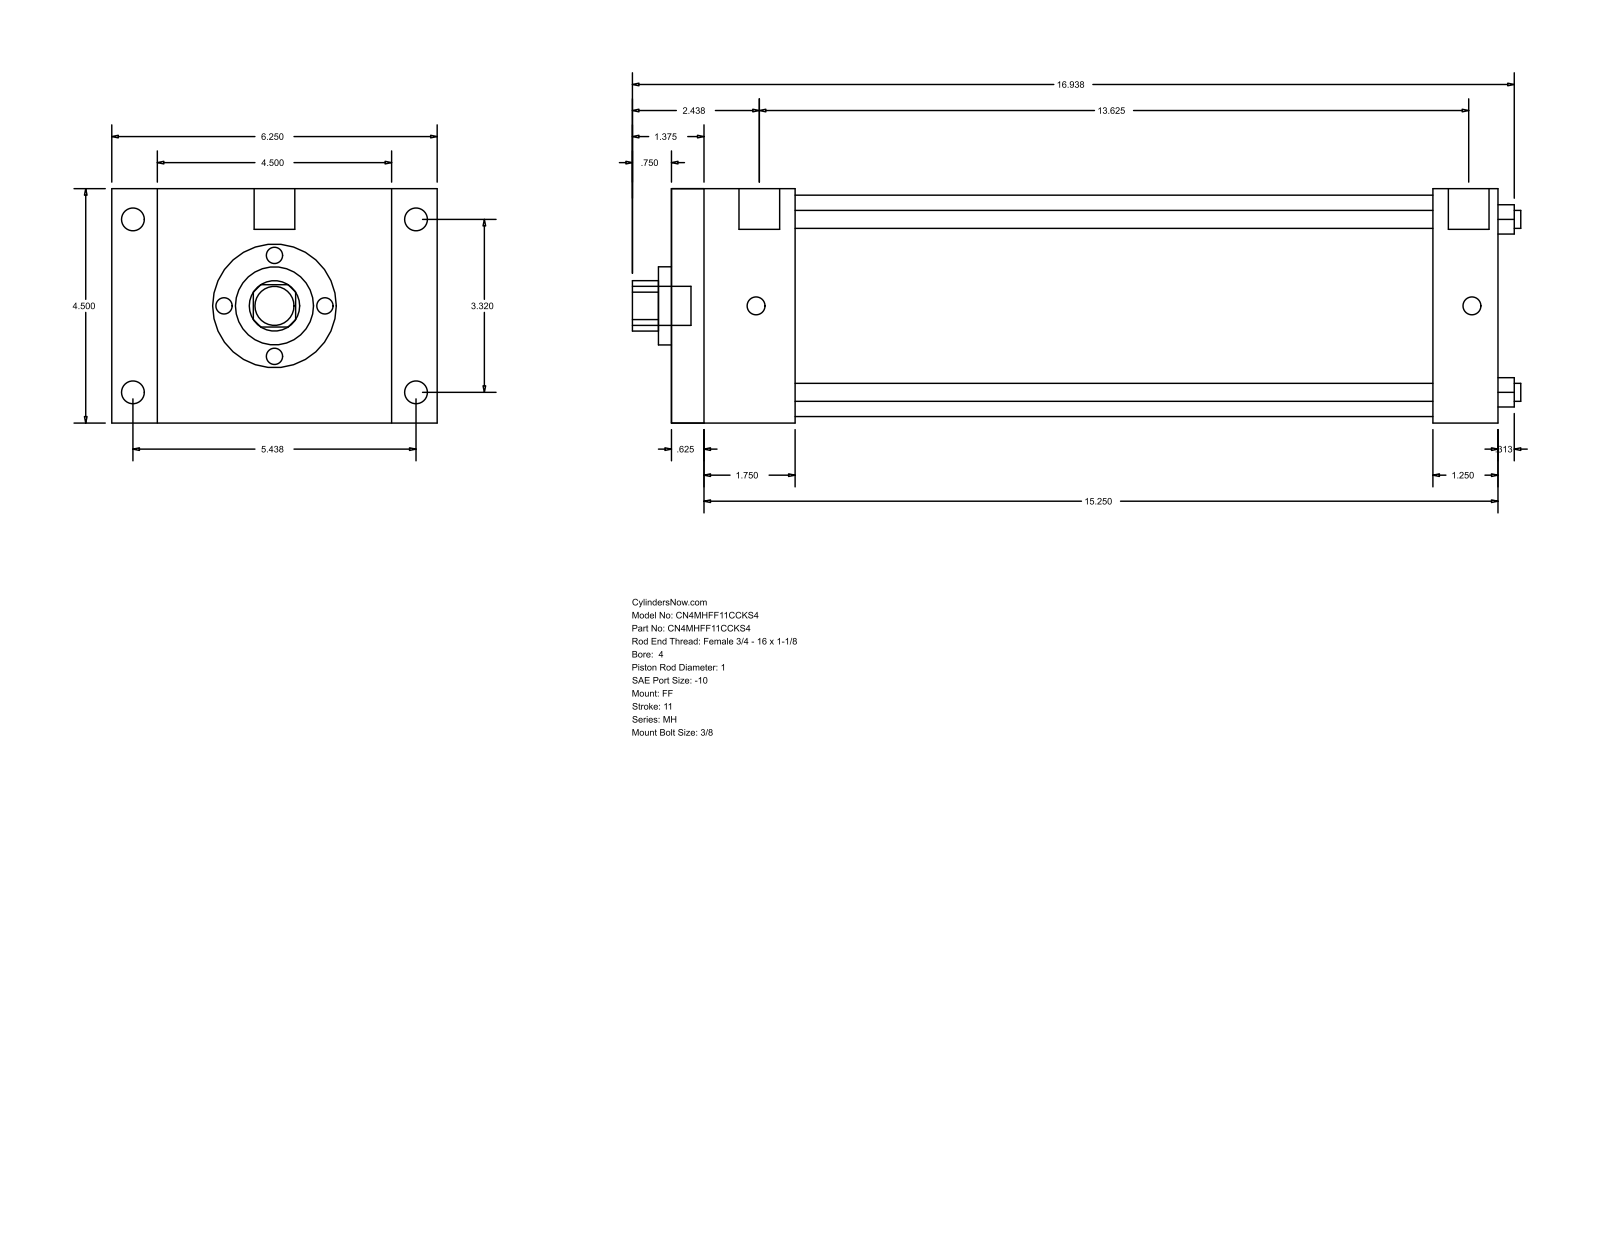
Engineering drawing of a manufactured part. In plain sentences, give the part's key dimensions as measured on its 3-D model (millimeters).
The part is named "MH_FF__0400_1". Its 3-D file was written by "GSSL Pune (CONFIG_CONTROL_DESIGN)". It is 0 solids with 92 faces: 64 planar, 28 cylindrical and 0 other. Overall it measures 433.39 by 158.75 by 114.3 millimeters. Round holes: 4 of diameter 8.76, 1 of diameter 25.4, 1 of diameter 38.1, 1 of diameter 107.95. Round bosses or shafts: 4 of diameter 11.13, 4 of diameter 8.73, 2 of diameter 19.84, 1 of diameter 19.05. Partial cylindrical surfaces (rounded edges, fillets, slot ends): 1 of radius 12.29. The main face-to-face distances are 114.3, 403.22, 15.87, 387.35, 60.33, 44.46, 342.89, 371.47, 355.6, 311.14. The hole center spacings are 59.62, 84.32, 119.25.
